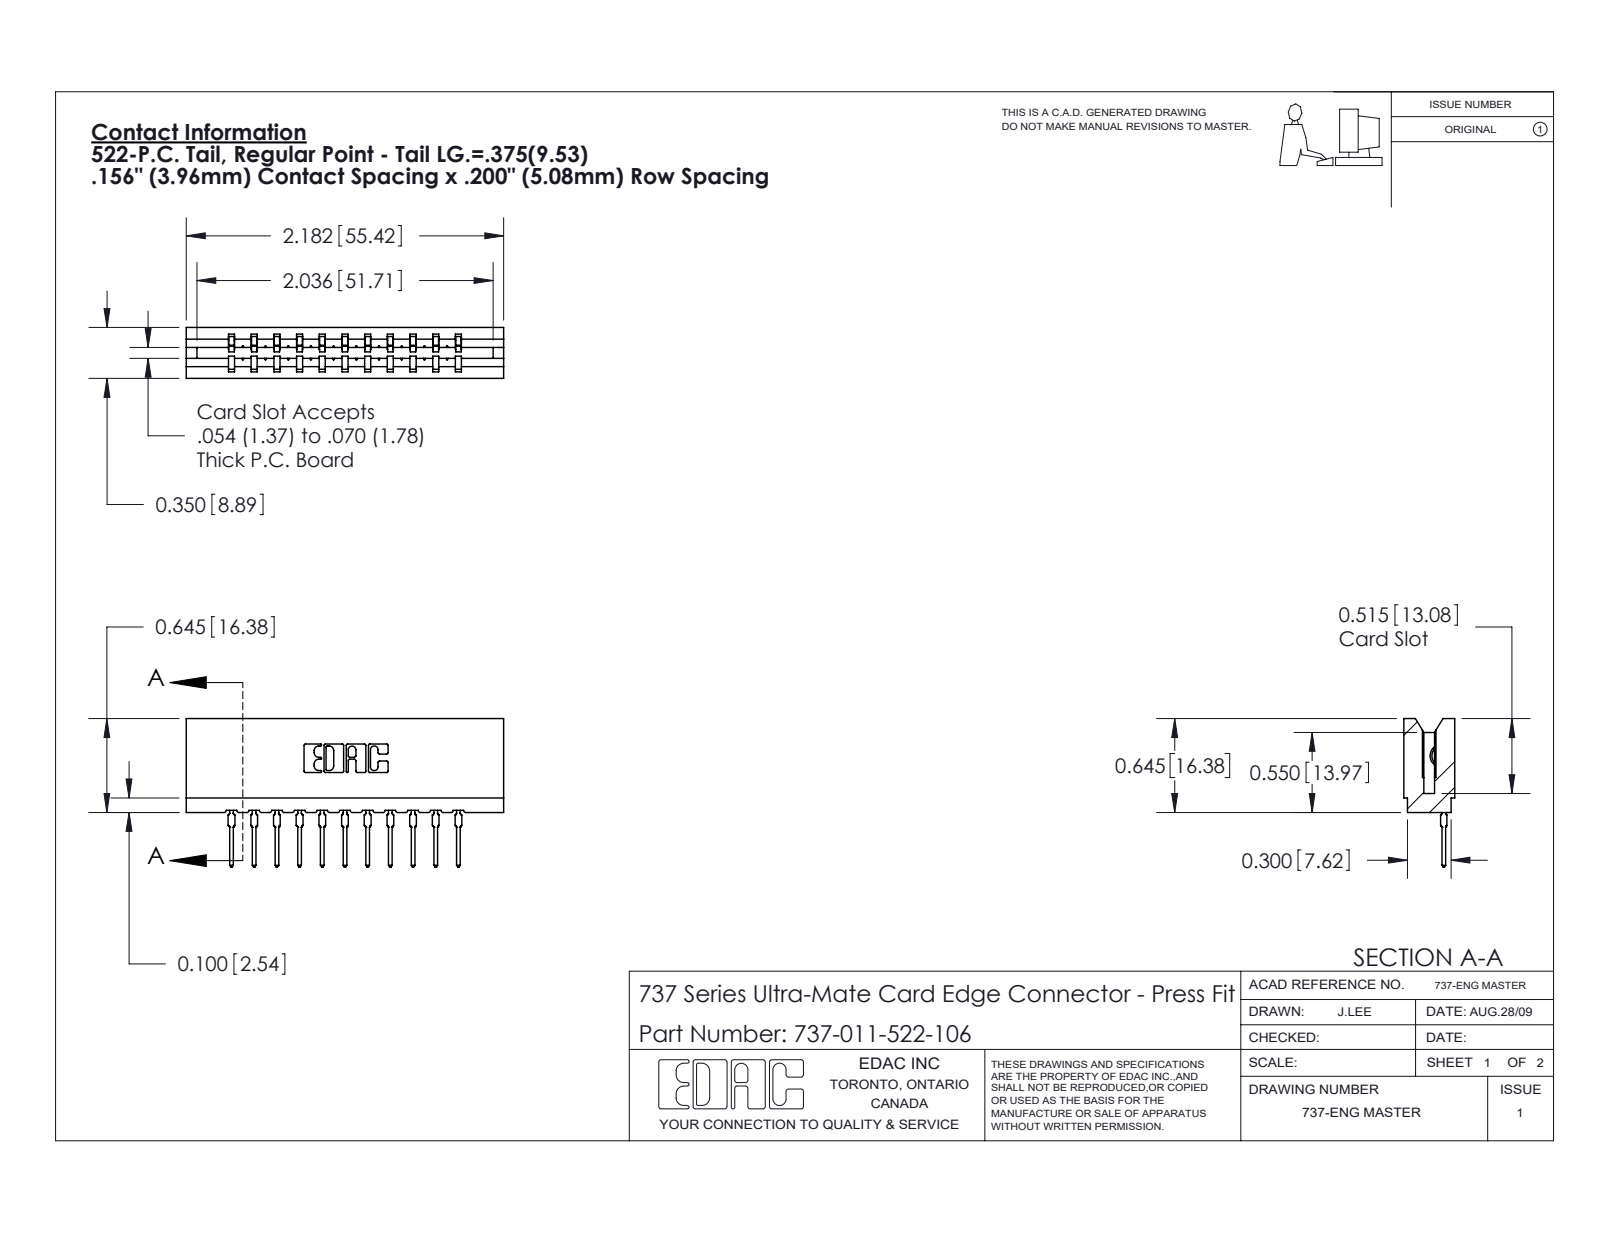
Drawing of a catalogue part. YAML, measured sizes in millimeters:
part_name: "737-011-522-106; 737 Part_Insulator Option - 06; 745-292-001_522"
step_written_by: "SolidWorks 2020 (CONFIG_CONTROL_DESIGN)"
units: millimeters
bodies: {solids: 12, faces: 1338, planar: 803, cylindrical: 249, other: 286}
overall_size: [55.4, 25.9, 8.9]
volume: 5560
surface_area: 6929
partial_cylinders:
  - {radius: 0.3, count: 22}
  - {radius: 0.4, count: 22}
  - {radius: 0.5, count: 22}
  - {radius: 0.2, count: 6}
  - {radius: 0.8, count: 6}
  - {radius: 0.1, count: 4}
  - {radius: 0.3, count: 4}
  - {radius: 0.7, count: 3}
face_to_face_distances: [4, 3.5, 5.4, 8.9, 15.8, 9, 7.9, 19.8, 11.9, 1.9]
